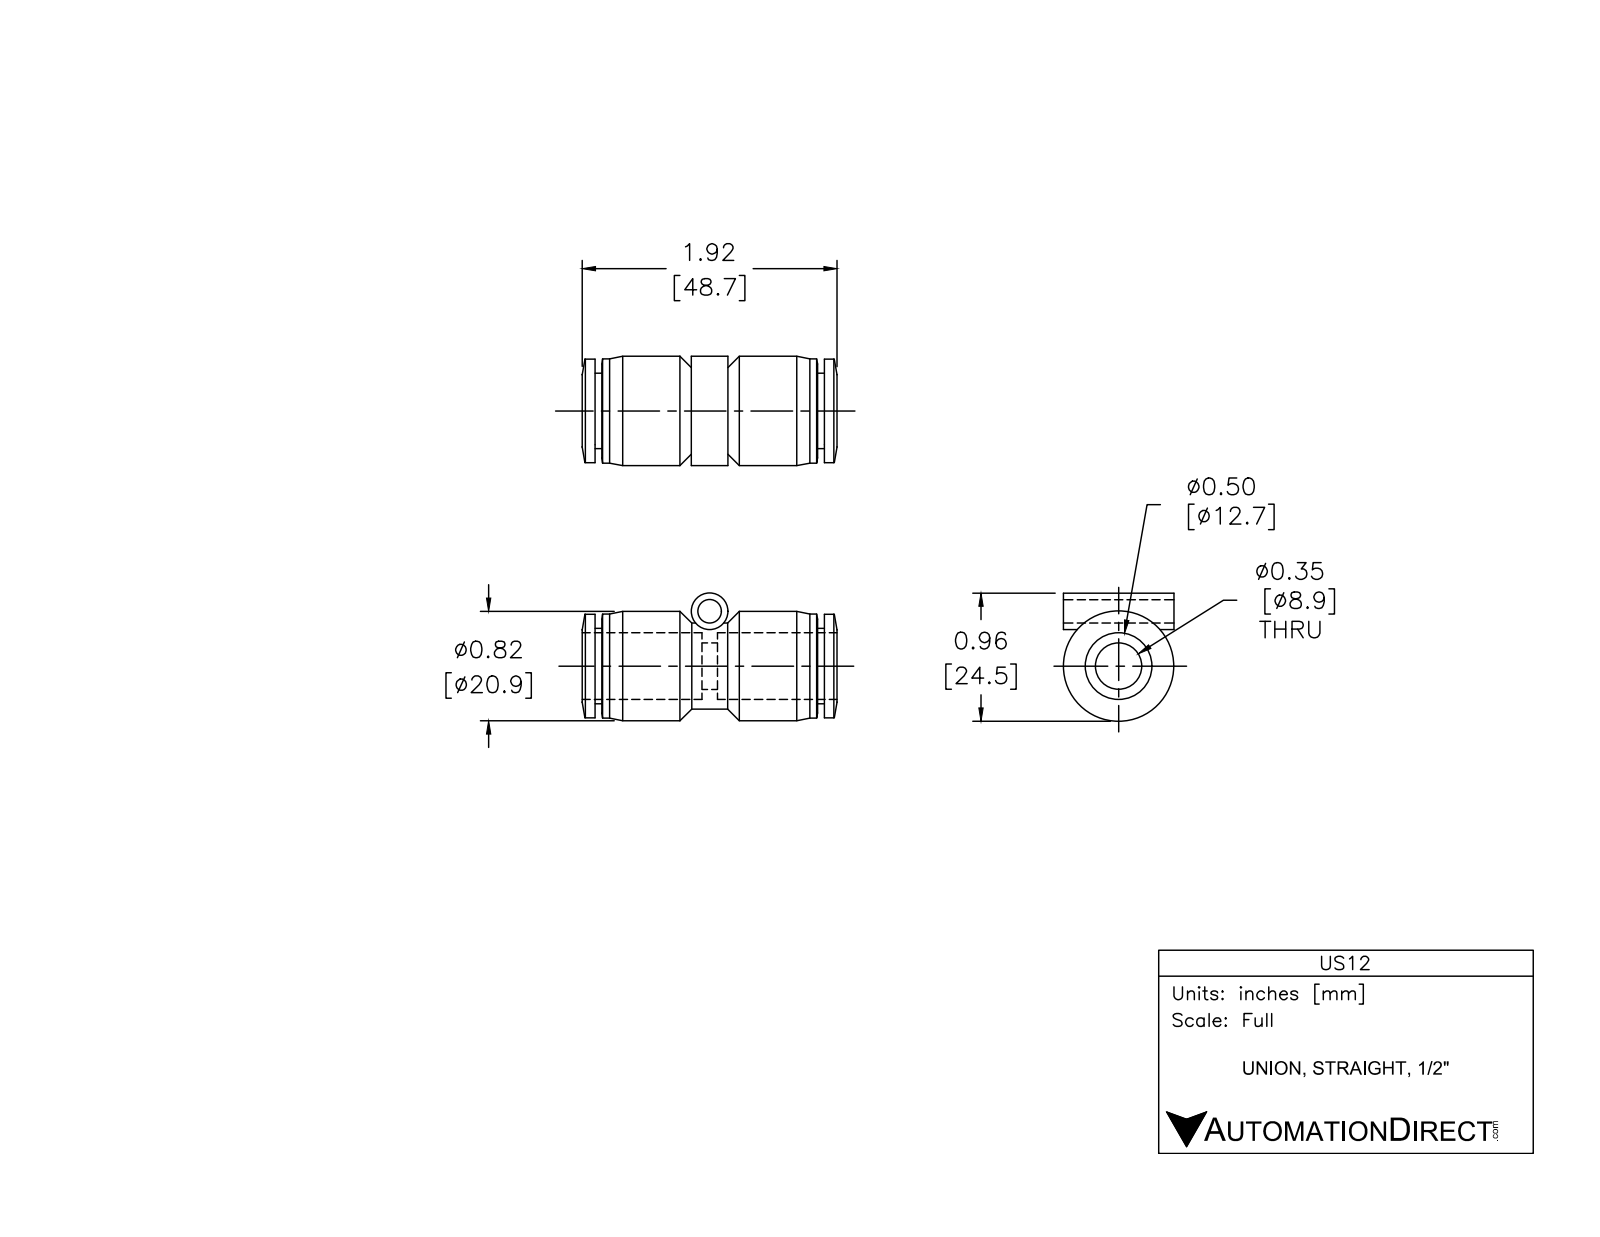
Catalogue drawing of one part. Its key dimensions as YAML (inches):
part_name: "US12"
step_written_by: "SolidWorks 2015 (AUTOMOTIVE_DESIGN)"
units: inches
bodies: {solids: 1, faces: 64, planar: 8, cylindrical: 28, other: 28}
overall_size: [1.925, 0.965, 0.827]
volume: 0.545
surface_area: 10.49
round_holes:
  - {diameter: 0.177, count: 1}
  - {diameter: 0.394, count: 1}
  - {diameter: 0.51, count: 1}
round_bosses_or_shafts:
  - {diameter: 0.827, count: 1}
  - {diameter: 0.787, count: 1}
  - {diameter: 0.783, count: 1}
  - {diameter: 0.65, count: 1}
  - {diameter: 0.569, count: 1}
  - {diameter: 0.276, count: 1}
face_to_face_distances: [0.051, 1.681, 1.732, 0.813, 0.919, 0.762, 0.868, 1.63, 0.106, 0.827]
